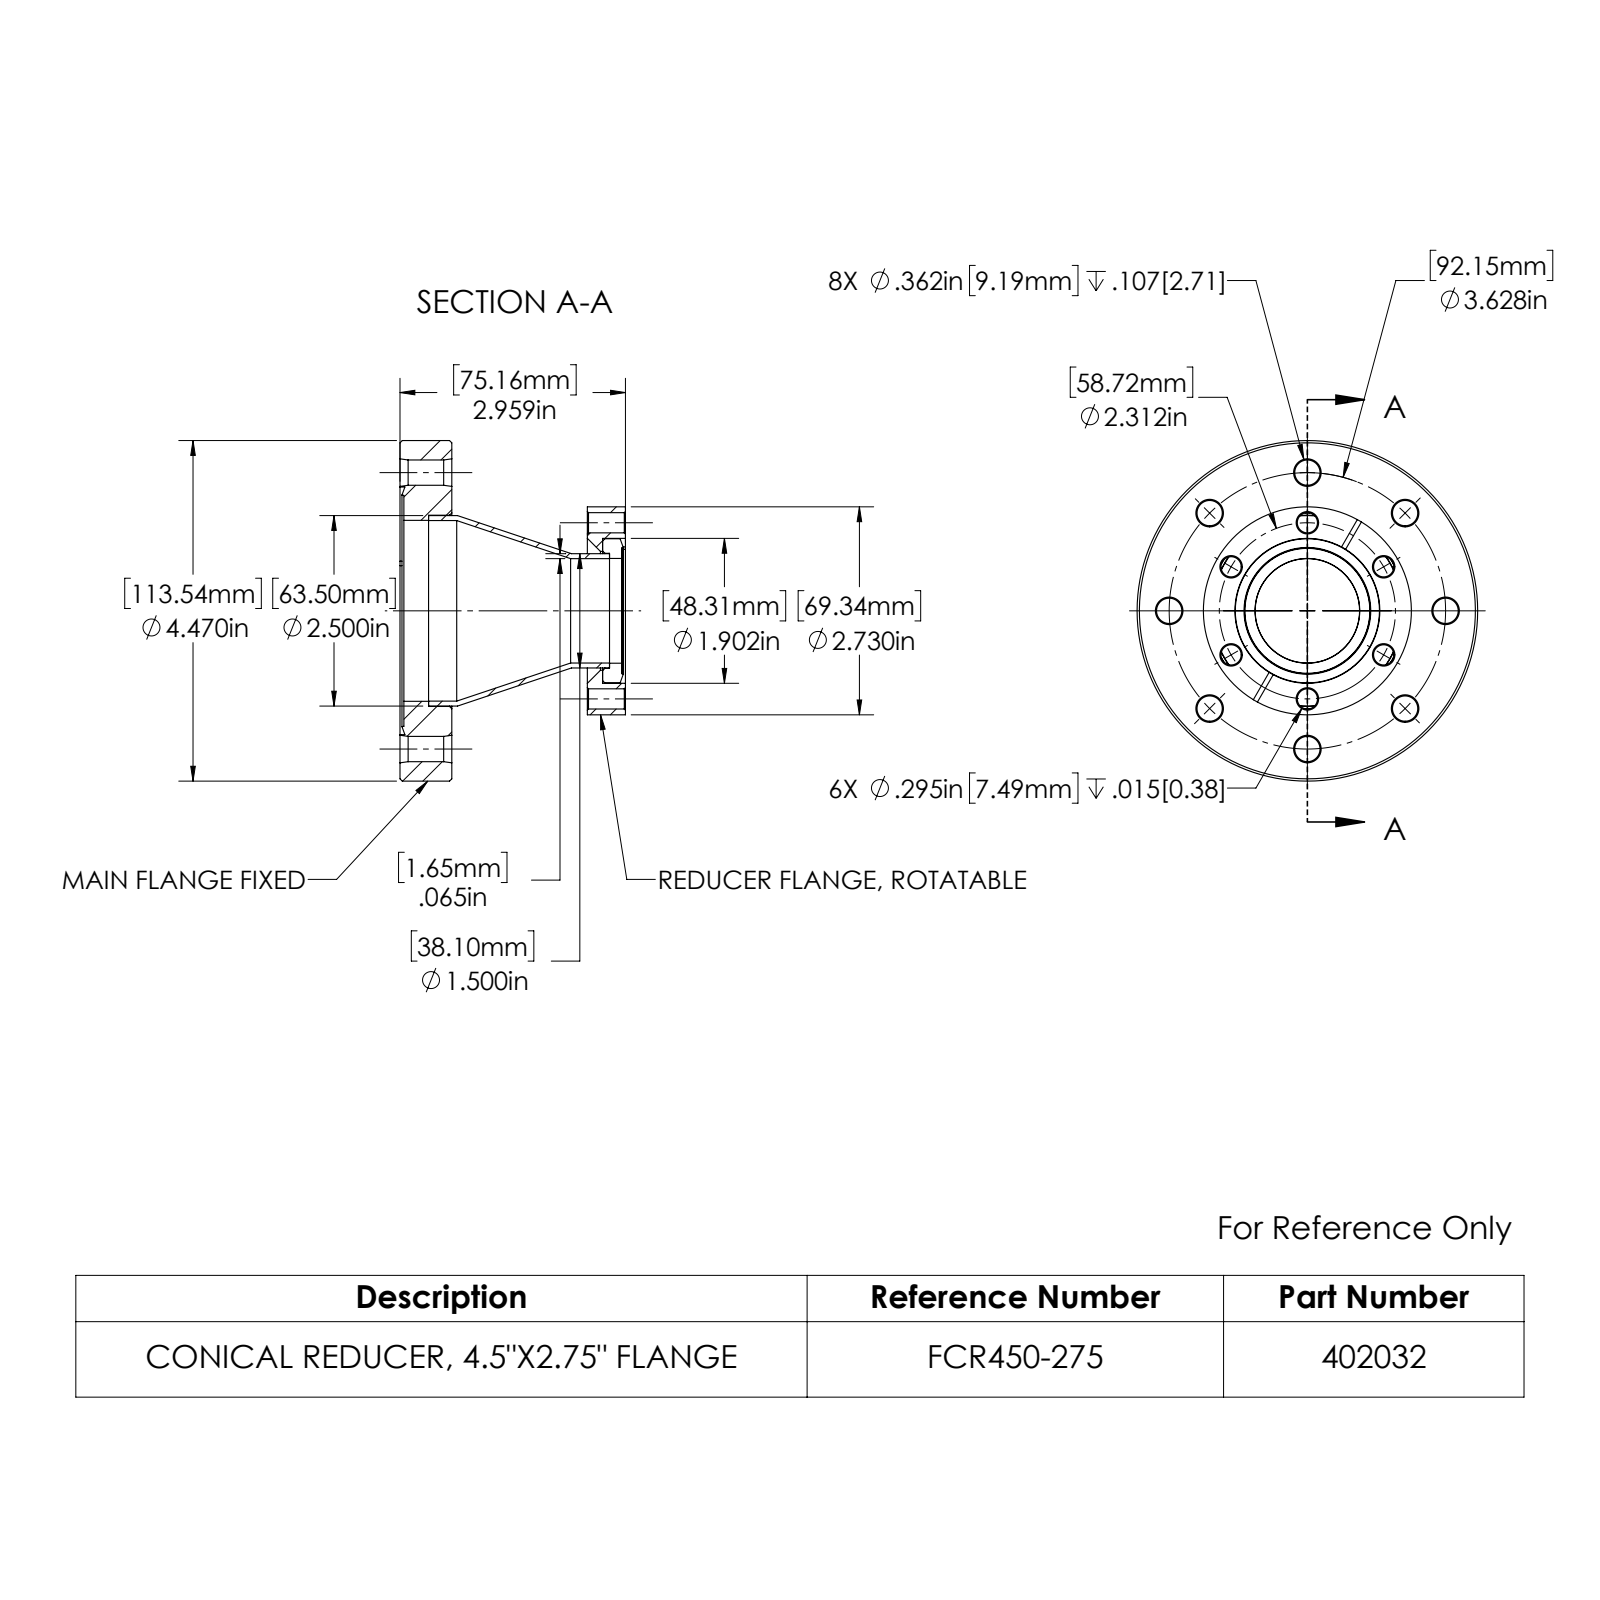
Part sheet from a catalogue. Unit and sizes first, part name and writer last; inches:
Units: inches
Overall size (bounding box): 4.47 × 4.47 × 2.959
Round holes (diameter × count): ⌀0.332 ×8, ⌀0.265 ×6, ⌀1.37 ×1, ⌀1.375 ×1, ⌀1.51 ×1, ⌀1.56 ×1, ⌀1.65 ×1, ⌀1.902 ×1, ⌀2.37 ×1, ⌀2.375 ×1, ⌀2.51 ×1, ⌀3.25 ×1
Round bosses / shafts (diameter × count): ⌀4.47 ×1, ⌀2.73 ×1, ⌀2.5 ×1, ⌀1.892 ×1, ⌀1.5 ×1
Main face-to-face distances: 0.68, 0.051, 0.629, 2.459, 2.408, 1.779, 2.959, 2.908, 2.279, 0.5
Hole centre spacings: 1.156, 1.814, 1.389, 2.565, 3.352, 0.759, 1.289, 1.591
Volume: 9.507 in³ · Surface area: 93.07 in²
Bodies: 4 solids, 169 faces (26 planar, 58 cylindrical, 85 other)
Part name (STEP PRODUCT): 110021; 402505; 910014; 402032 (+1 more)
STEP written by: SolidWorks 2022 (AUTOMOTIVE_DESIGN)
